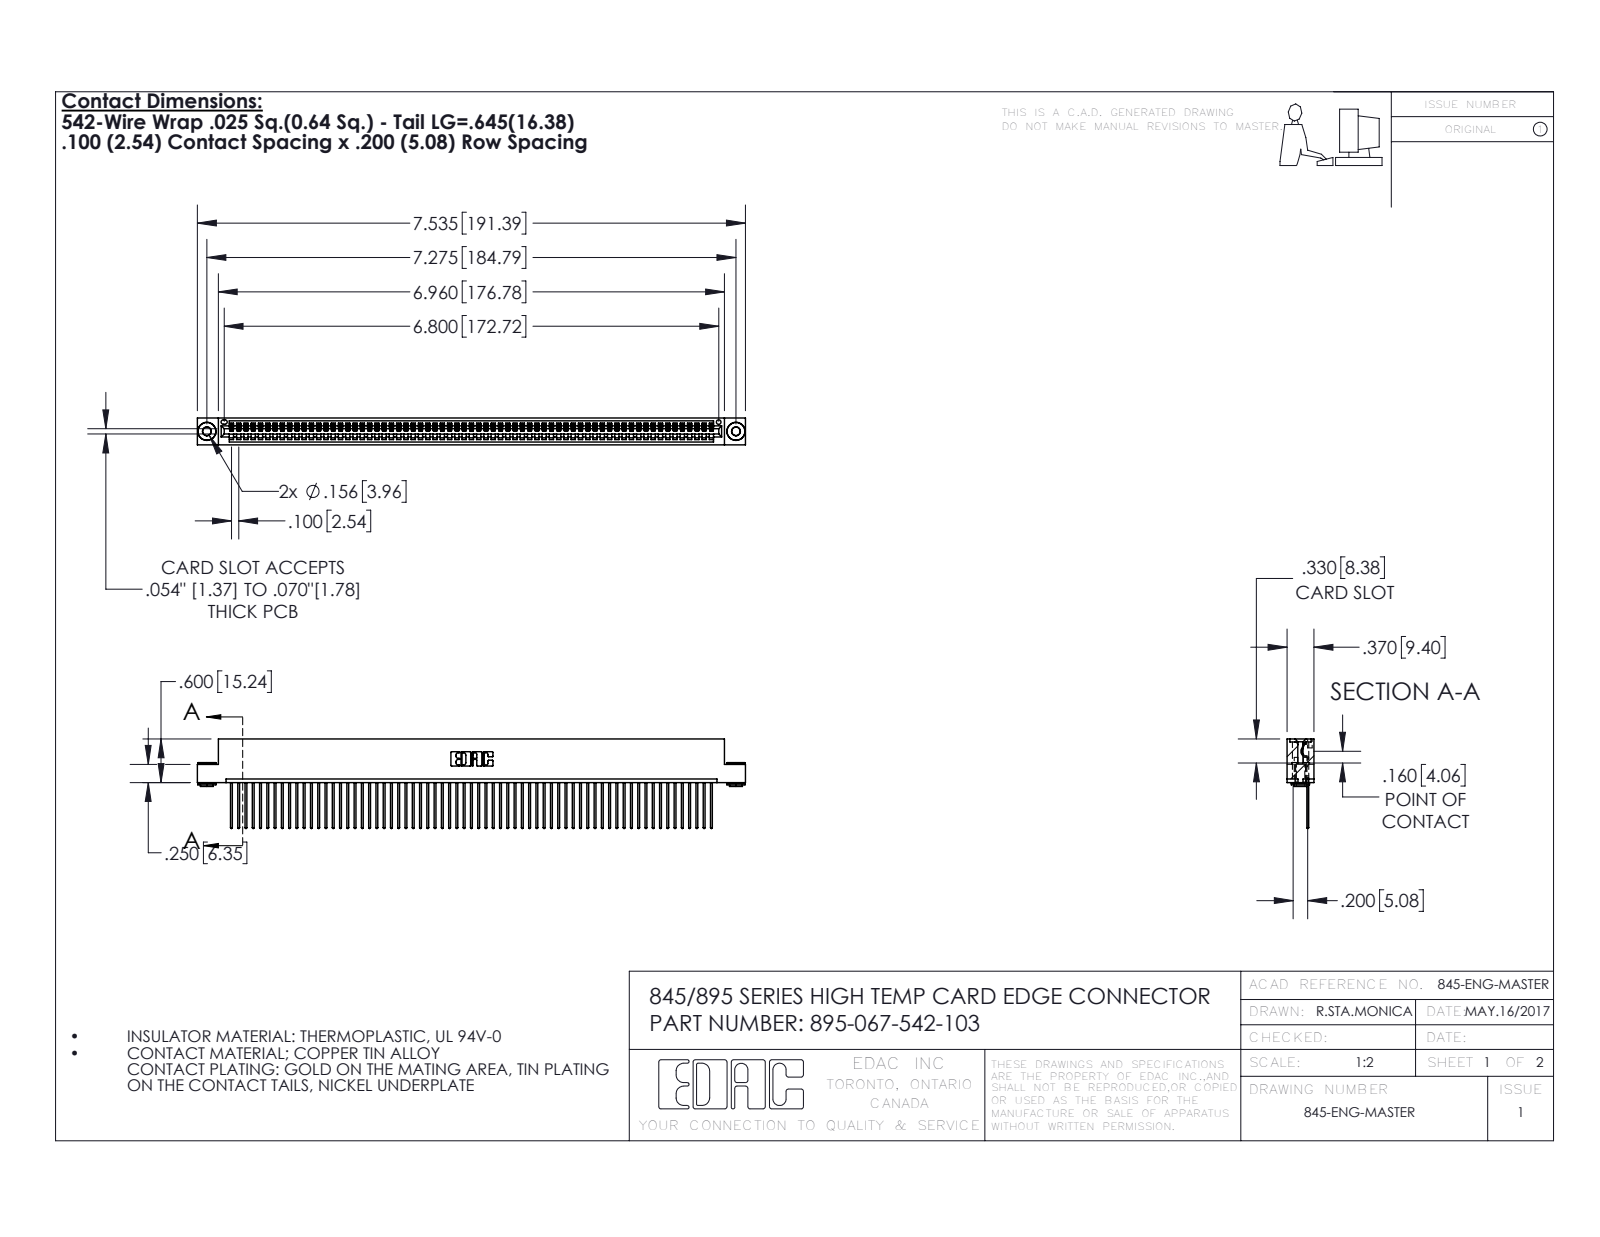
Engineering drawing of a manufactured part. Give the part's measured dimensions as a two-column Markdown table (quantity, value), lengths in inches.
| quantity | value |
| --- | --- |
| part name | 395-067-542-103; 345 Part_Flush Mounting Lugs - 0.156 Dia-TH; 345-250-002_345-250-002-102; 345-292-001_345-293-142 |
| STEP written by | SolidWorks 2016 (CONFIG_CONTROL_DESIGN) |
| units | inches |
| bodies | 70 solids, 4050 faces (2770 planar, 1272 cylindrical, 8 other) |
| overall size | 7.535 × 1.232 × 0.37 |
| volume | 1.132 in³ |
| surface area | 40.53 in² |
| round holes (diameter × count) | 0.116 × 2, 0.156 × 2, 0.064 × 1 |
| round bosses / shafts (diameter × count) | 0.25 × 2, 0.18 × 2, 0.136 × 2 |
| partial cylindrical surfaces (radius × count) | 0.006 × 134, 0.01 × 134, 0.01 × 22, 0.007 × 6, 0.031 × 6, 0.026 × 3, 0.031 × 2, 0.04 × 2 |
| main face-to-face distances | 0.072, 0.298, 0.025, 0.098, 0.272, 0.37, 0.2, 0.225, 0.149, 0.072 |
| hole center spacings | 0.27, 7.039, 7.275 |
